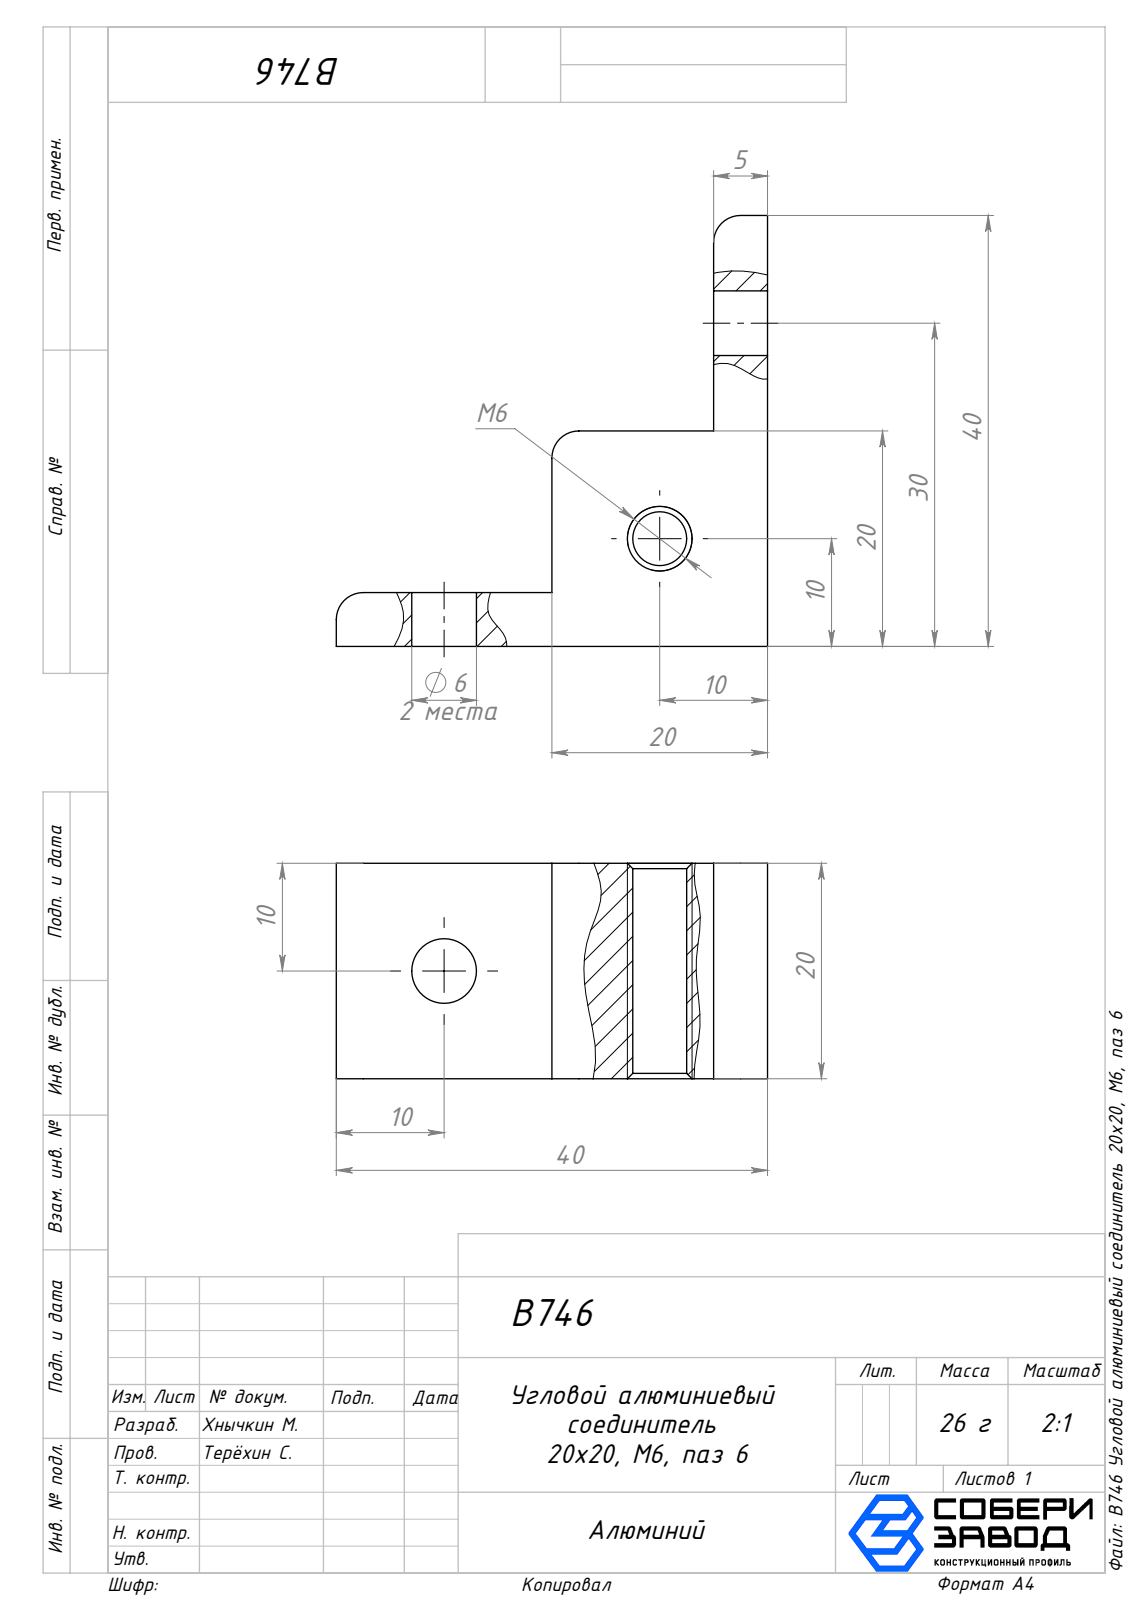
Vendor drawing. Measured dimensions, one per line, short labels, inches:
name: B746 Угловой алюминиевый соединитель 20х20, M6, паз 6
written by: SolidWorks 2025 (AUTOMOTIVE_DESIGN)
unit: in
bodies: 1 solid, 23 faces (10 planar, 9 cylindrical, 4 other)
size: 1.575 × 1.575 × 0.787
volume: 0.686 in³; area: 7.237 in²
holes: 2× ⌀0.236, 1× ⌀0.197
rounds: 3× R0.098
face distances: 0.787, 0.197, 0.591, 1.575, 1.378
